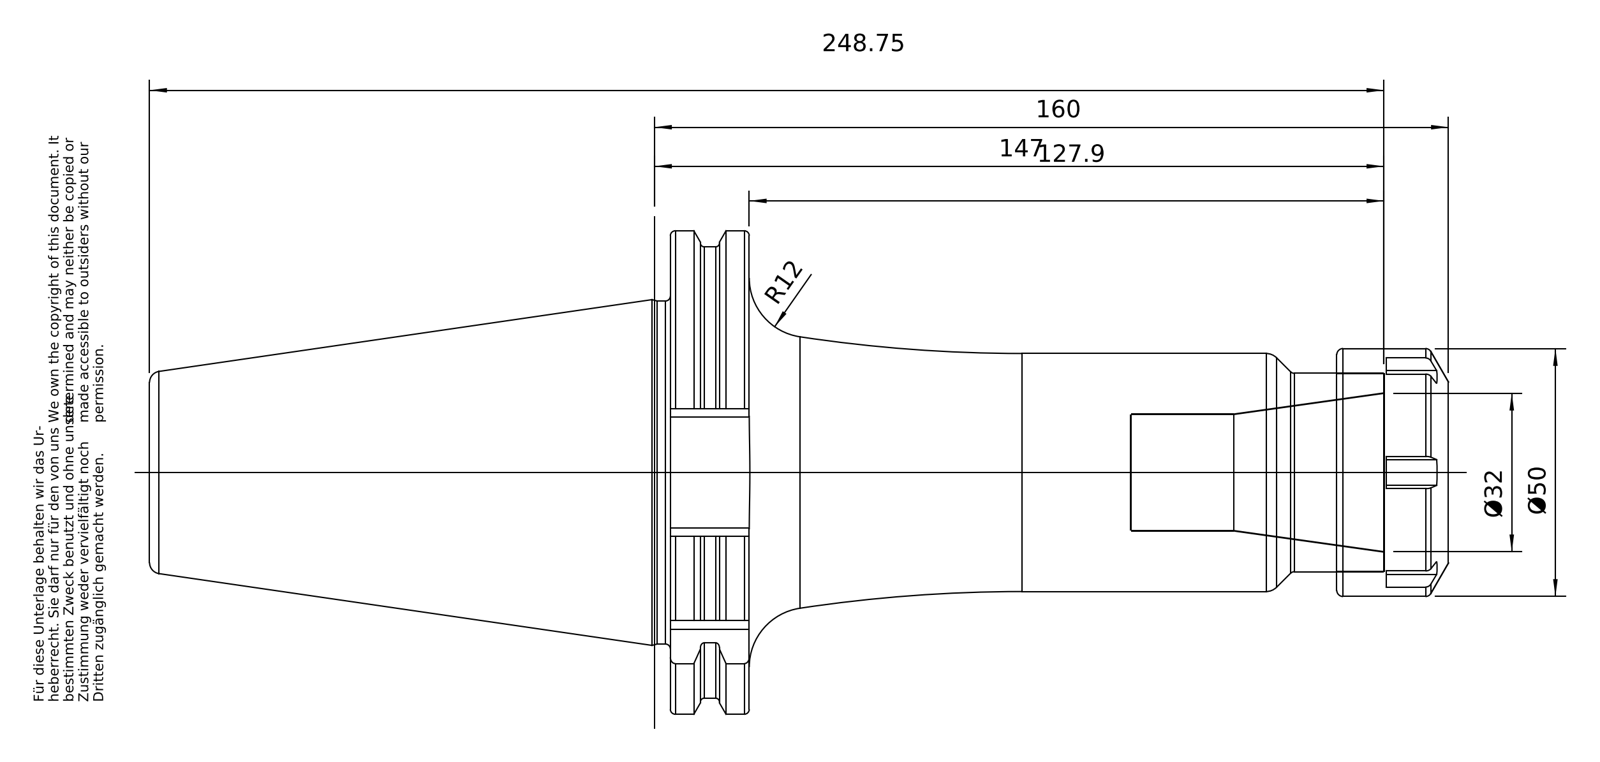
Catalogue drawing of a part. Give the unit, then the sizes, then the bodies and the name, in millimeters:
Units: millimetres
Overall size (bounding box): 261.6 × 97.47 × 94
Round holes (diameter × count): ⌀20.75 ×1, ⌀23.5 ×1, ⌀25.01 ×1, ⌀25.7 ×1
Round bosses / shafts (diameter × count): ⌀91 ×1, ⌀69.15 ×1, ⌀50 ×1, ⌀48 ×1, ⌀40 ×1, ⌀24.01 ×1
Partial cylindrical surfaces — rounded edges, fillets, slot ends (radius × count): R2.7 ×6, R1.75 ×5, R48.74 ×1
Main face-to-face distances: 15.85, 134.3, 118.45, 156.8, 140.95, 22.5, 143.8, 127.95, 9.5, 13
Volume: 591 672 mm³ · Surface area: 71 247 mm²
Bodies: 2 solids, 150 faces (48 planar, 38 cylindrical, 64 other)
Part name (STEP PRODUCT): 50-322-32; 83-912-32; 50-322-32_ASM
STEP written by: PRO/ENGINEER BY PARAMETRIC TECHNOLOGY CORPORATION, 2010430 (CONFIG_CONTROL_DESIGN)
